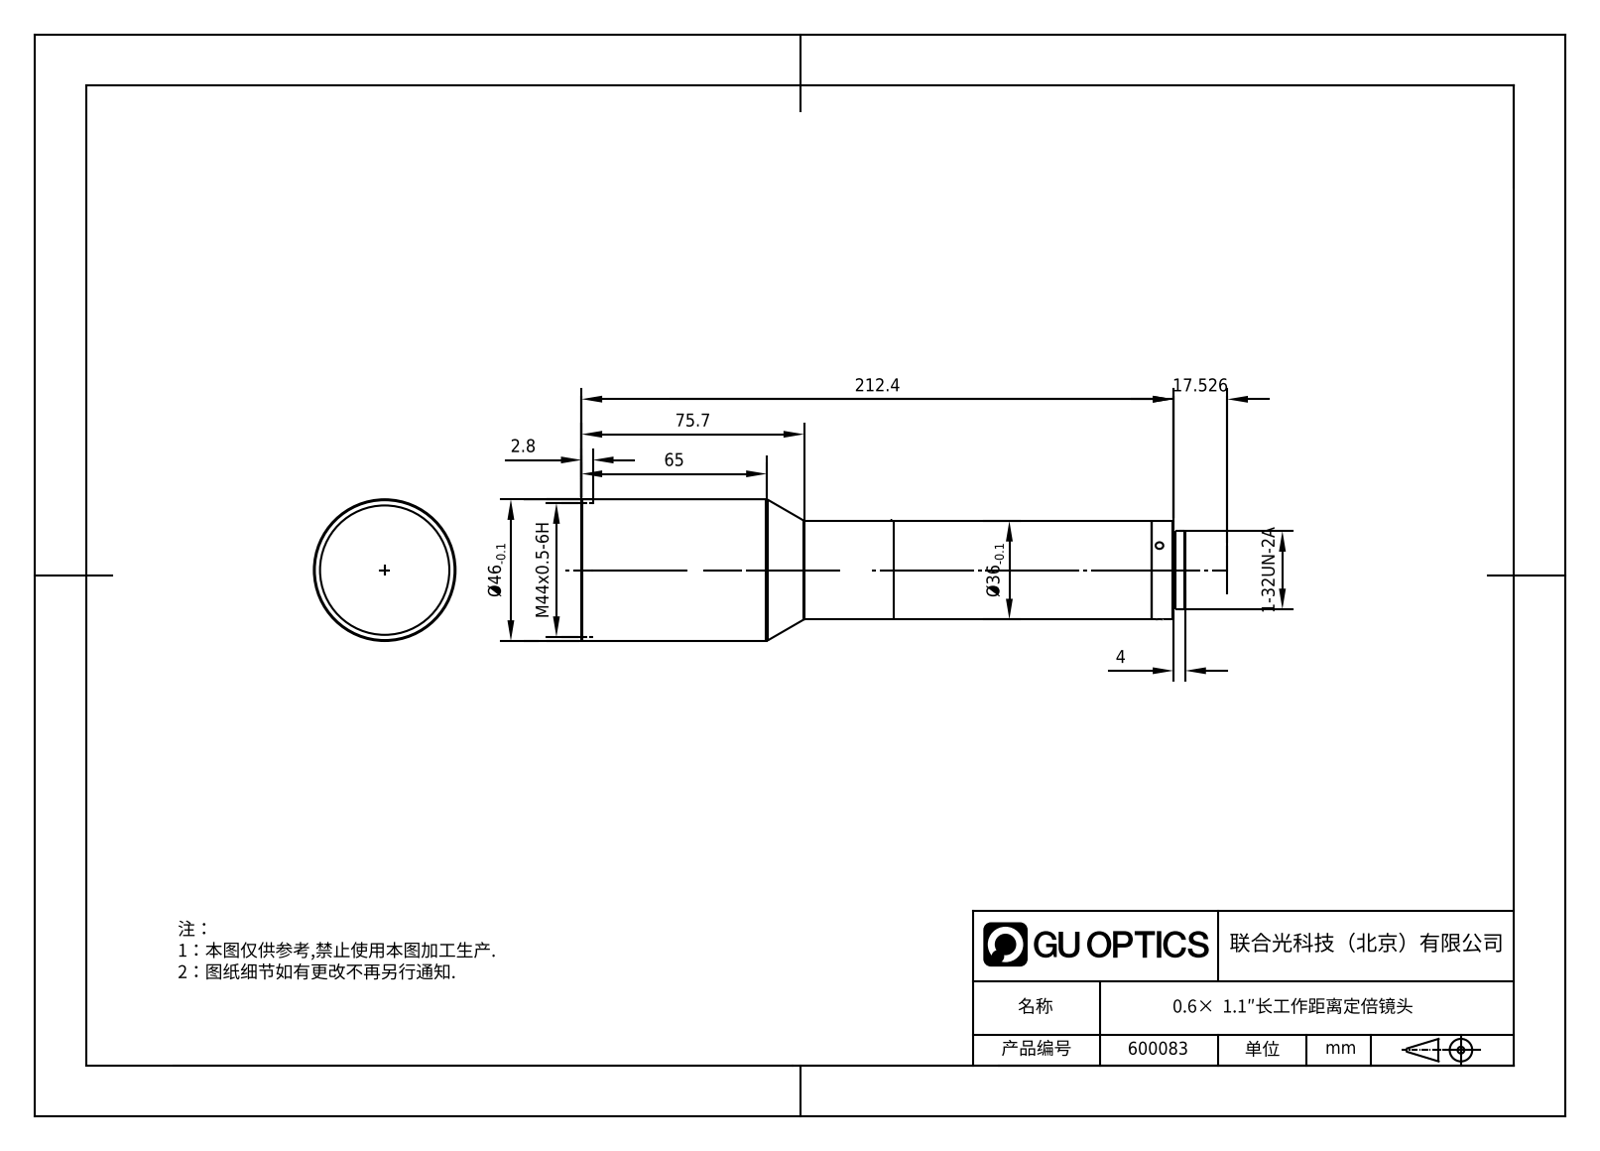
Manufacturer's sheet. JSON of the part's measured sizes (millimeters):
{"part_name": "600083", "step_written_by": "SolidWorks 2020 (CONFIG_CONTROL_DESIGN)", "units": "millimeters", "bodies": {"solids": 2, "faces": 32, "planar": 9, "cylindrical": 14, "other": 9}, "overall_size": [216.39, 46, 46], "volume_mm3": 257340, "surface_area_mm2": 34010, "round_holes": [[2.5, 3], [42, 1]], "round_bosses_or_shafts": [[46, 1], [36, 1], [33.5, 1], [25.4, 1], [24.6, 1]], "face_to_face_distances": [203.39, 4, 207.39, 216.39, 212.39, 9, 100.03, 96.03, 107.36, 116.36]}
